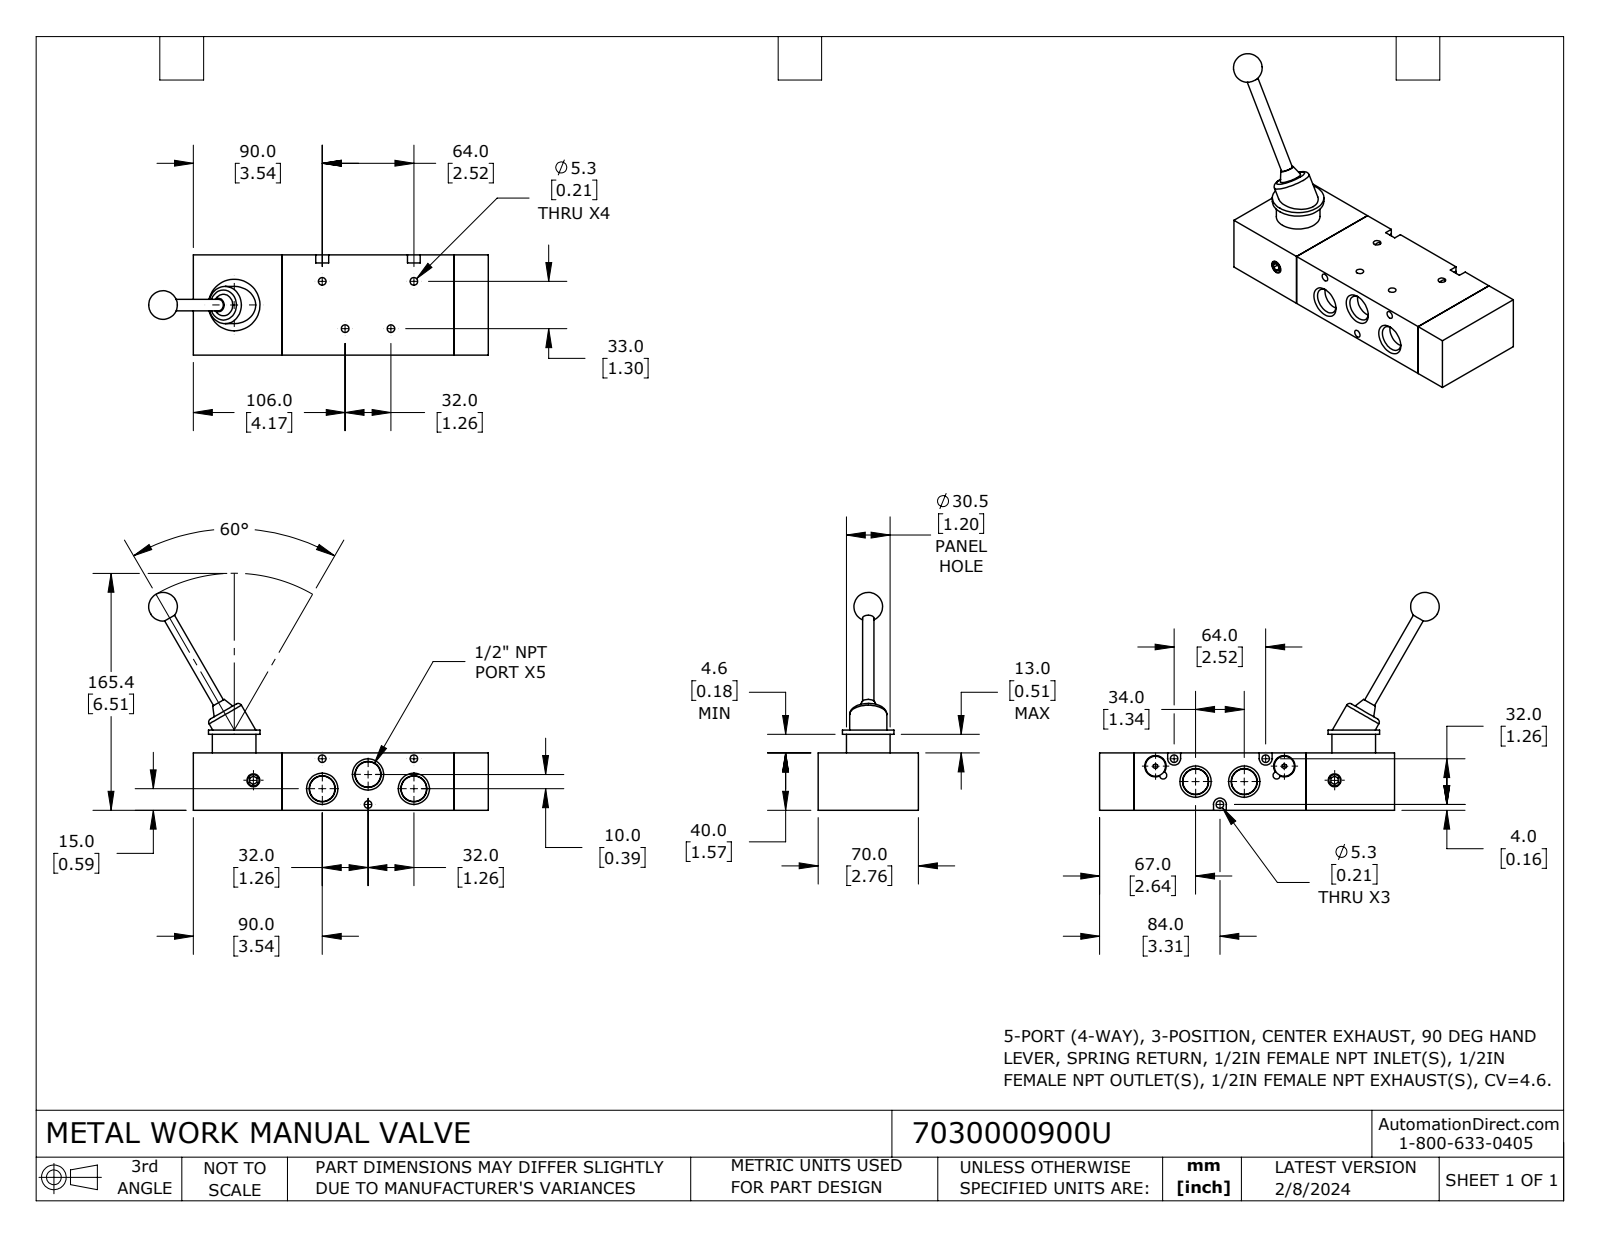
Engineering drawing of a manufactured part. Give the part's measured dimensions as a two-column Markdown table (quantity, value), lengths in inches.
| quantity | value |
| --- | --- |
| part name | 7030000900U |
| STEP written by | SolidWorks 2023 (CONFIG_CONTROL_DESIGN) |
| units | inches |
| bodies | 3 solids, 155 faces (72 planar, 57 cylindrical, 26 other) |
| overall size | 9.339 × 5.988 × 2.756 |
| volume | 35.65 in³ |
| surface area | 120.8 in² |
| round holes (diameter × count) | 0.209 × 7, 0.587 × 2, 0.354 × 1 |
| round bosses / shafts (diameter × count) | 0.551 × 2, 1.417 × 1, 1.201 × 1, 1.024 × 1, 0.315 × 1, 0.313 × 1 |
| partial cylindrical surfaces (radius × count) | 0.177 × 3, 0.098 × 2 |
| main face-to-face distances | 1.575, 2.756, 4.724, 0.945, 5.669, 8.11, 7.165, 2.441, 0.354, 2.402 |
| hole center spacings | 0.552, 1.444, 1.781, 2.061, 2.293, 2.52, 3.039, 1.26 |
